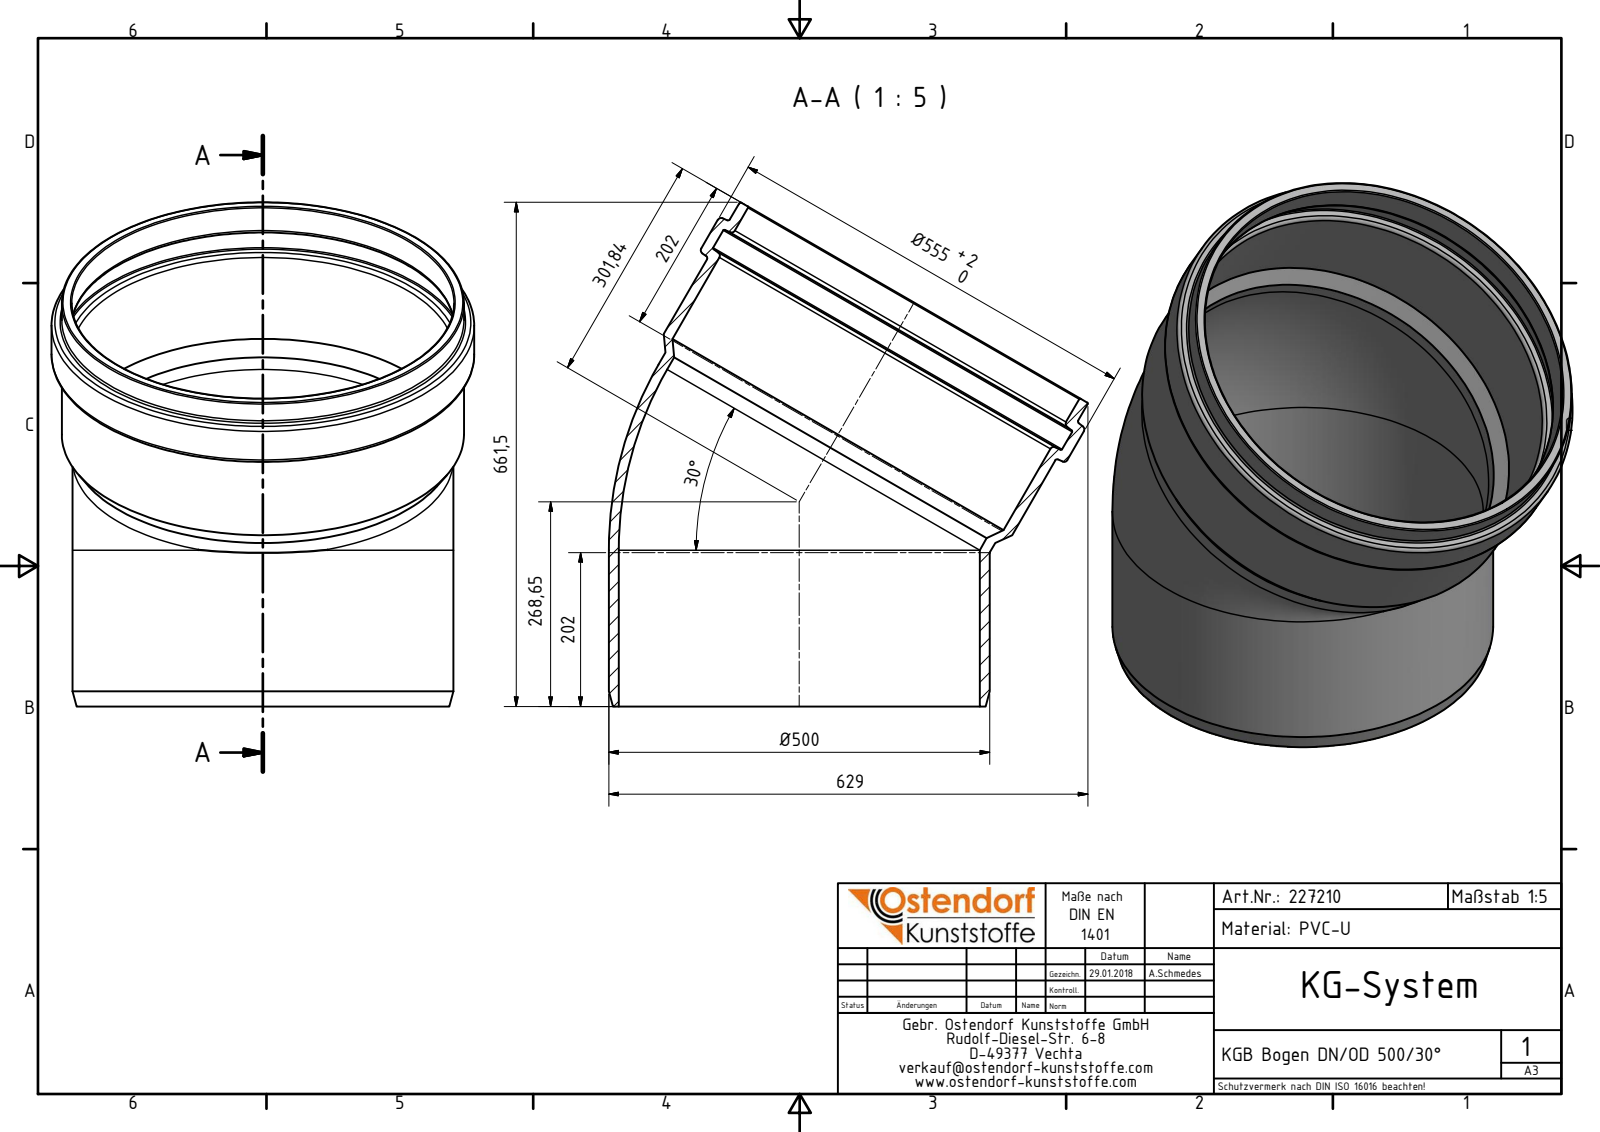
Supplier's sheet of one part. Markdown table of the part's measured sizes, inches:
| quantity | value |
| --- | --- |
| part name | 227210 KGB Bogen DN_OD 500_30° |
| STEP written by | Autodesk Inventor 2016 (AUTOMOTIVE_DESIGN) |
| units | inches |
| bodies | 1 solid, 32 faces (2 planar, 10 cylindrical, 20 other) |
| overall size | 26.043 × 24.764 × 21.85 |
| volume | 687.7 in³ |
| surface area | 2 933 in² |
| round holes (diameter × count) | 18.661 × 2, 19.764 × 2, 20.827 × 1 |
| round bosses / shafts (diameter × count) | 20.787 × 2, 19.685 × 2, 21.85 × 1 |
